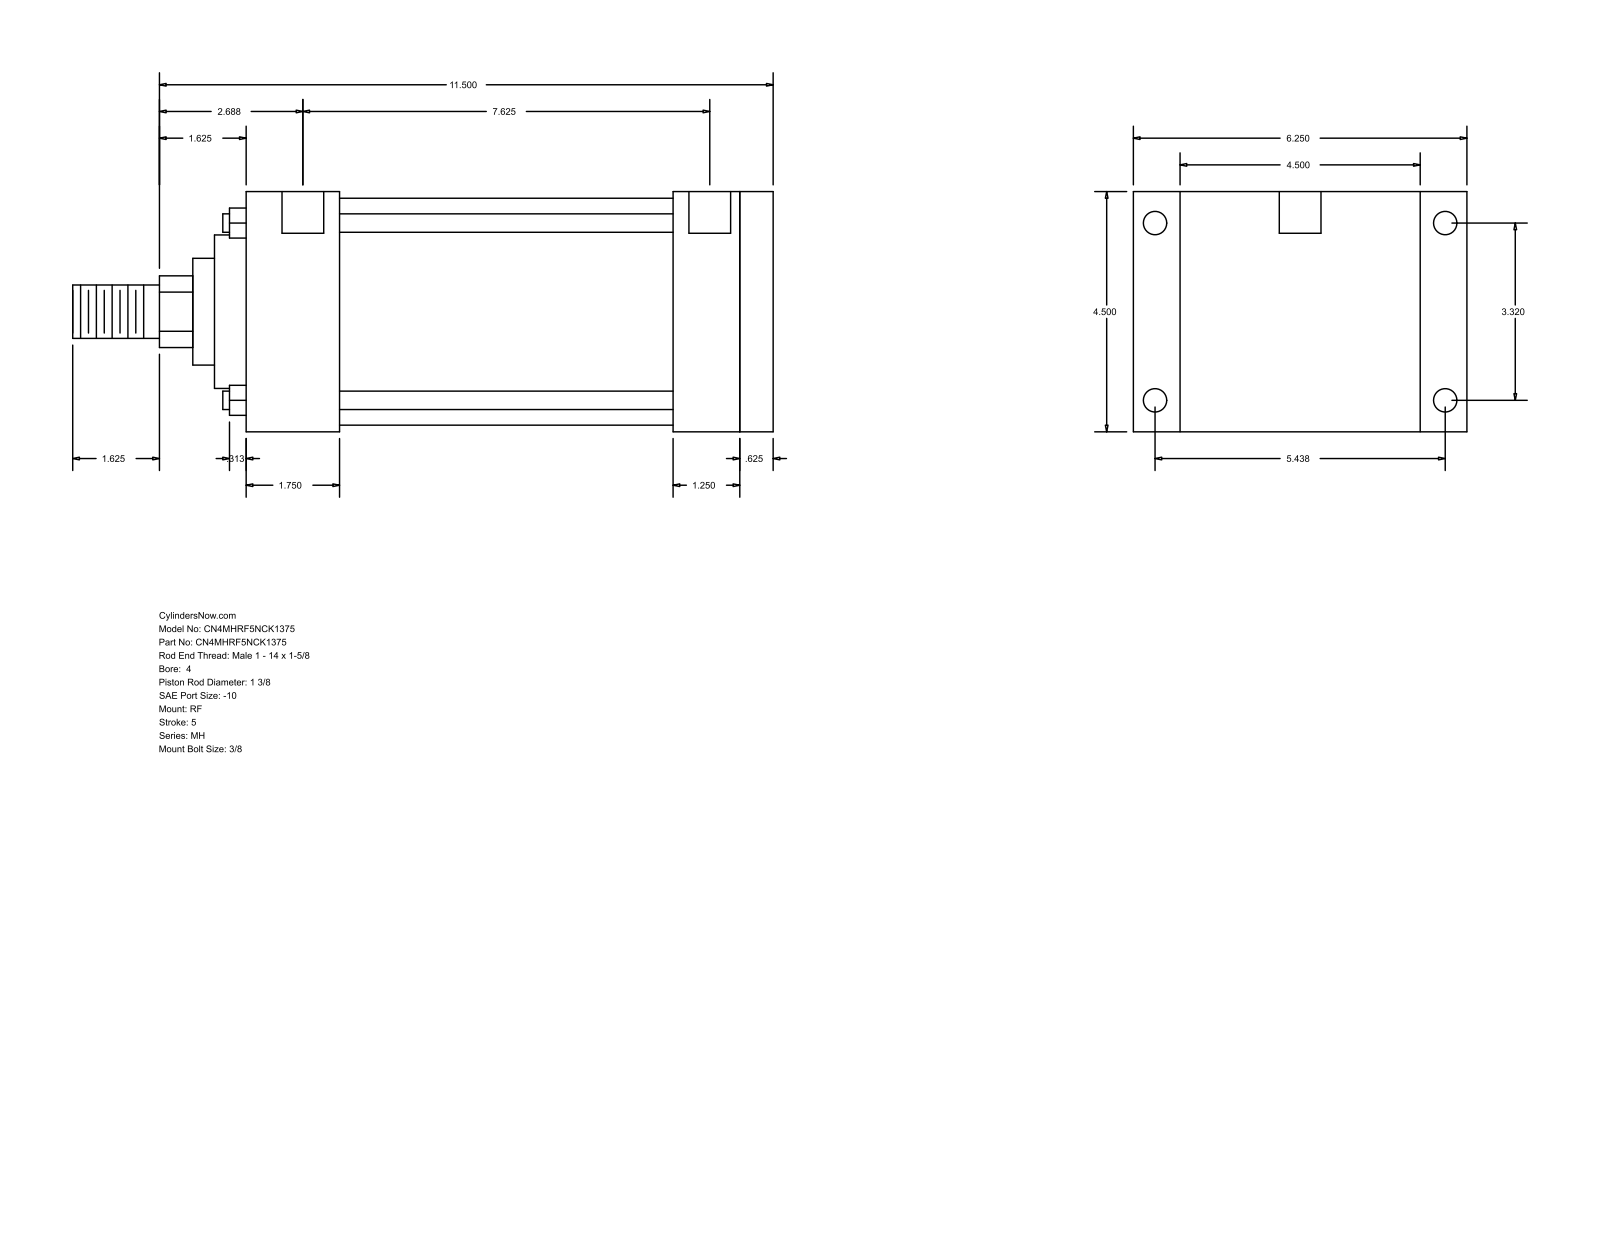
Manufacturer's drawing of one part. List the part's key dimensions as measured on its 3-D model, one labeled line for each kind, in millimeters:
Part name (STEP PRODUCT): MH_RF__0400_1.375
STEP written by: GSSL Pune (CONFIG_CONTROL_DESIGN)
Units: millimetres
Bodies: 0 solids, 94 faces (65 planar, 29 cylindrical, 0 other)
Overall size (bounding box): 333.38 × 158.75 × 114.3
Round holes (diameter × count): ⌀8.73 ×4, ⌀11.13 ×4, ⌀19.84 ×2
Round bosses / shafts (diameter × count): ⌀8.76 ×4, ⌀107.95 ×1, ⌀73.03 ×1, ⌀50.8 ×1, ⌀34.92 ×1, ⌀25.4 ×1
Partial cylindrical surfaces — rounded edges, fillets, slot ends (radius × count): R17.06 ×1
Main face-to-face distances: 114.3, 250.83, 234.96, 15.87, 44.45, 190.51, 206.38, 203.2, 158.75, 31.76
Hole centre spacings: 84.32, 138.12, 161.82, 196.85, 1.58, 1.59, 193.68, 195.26
